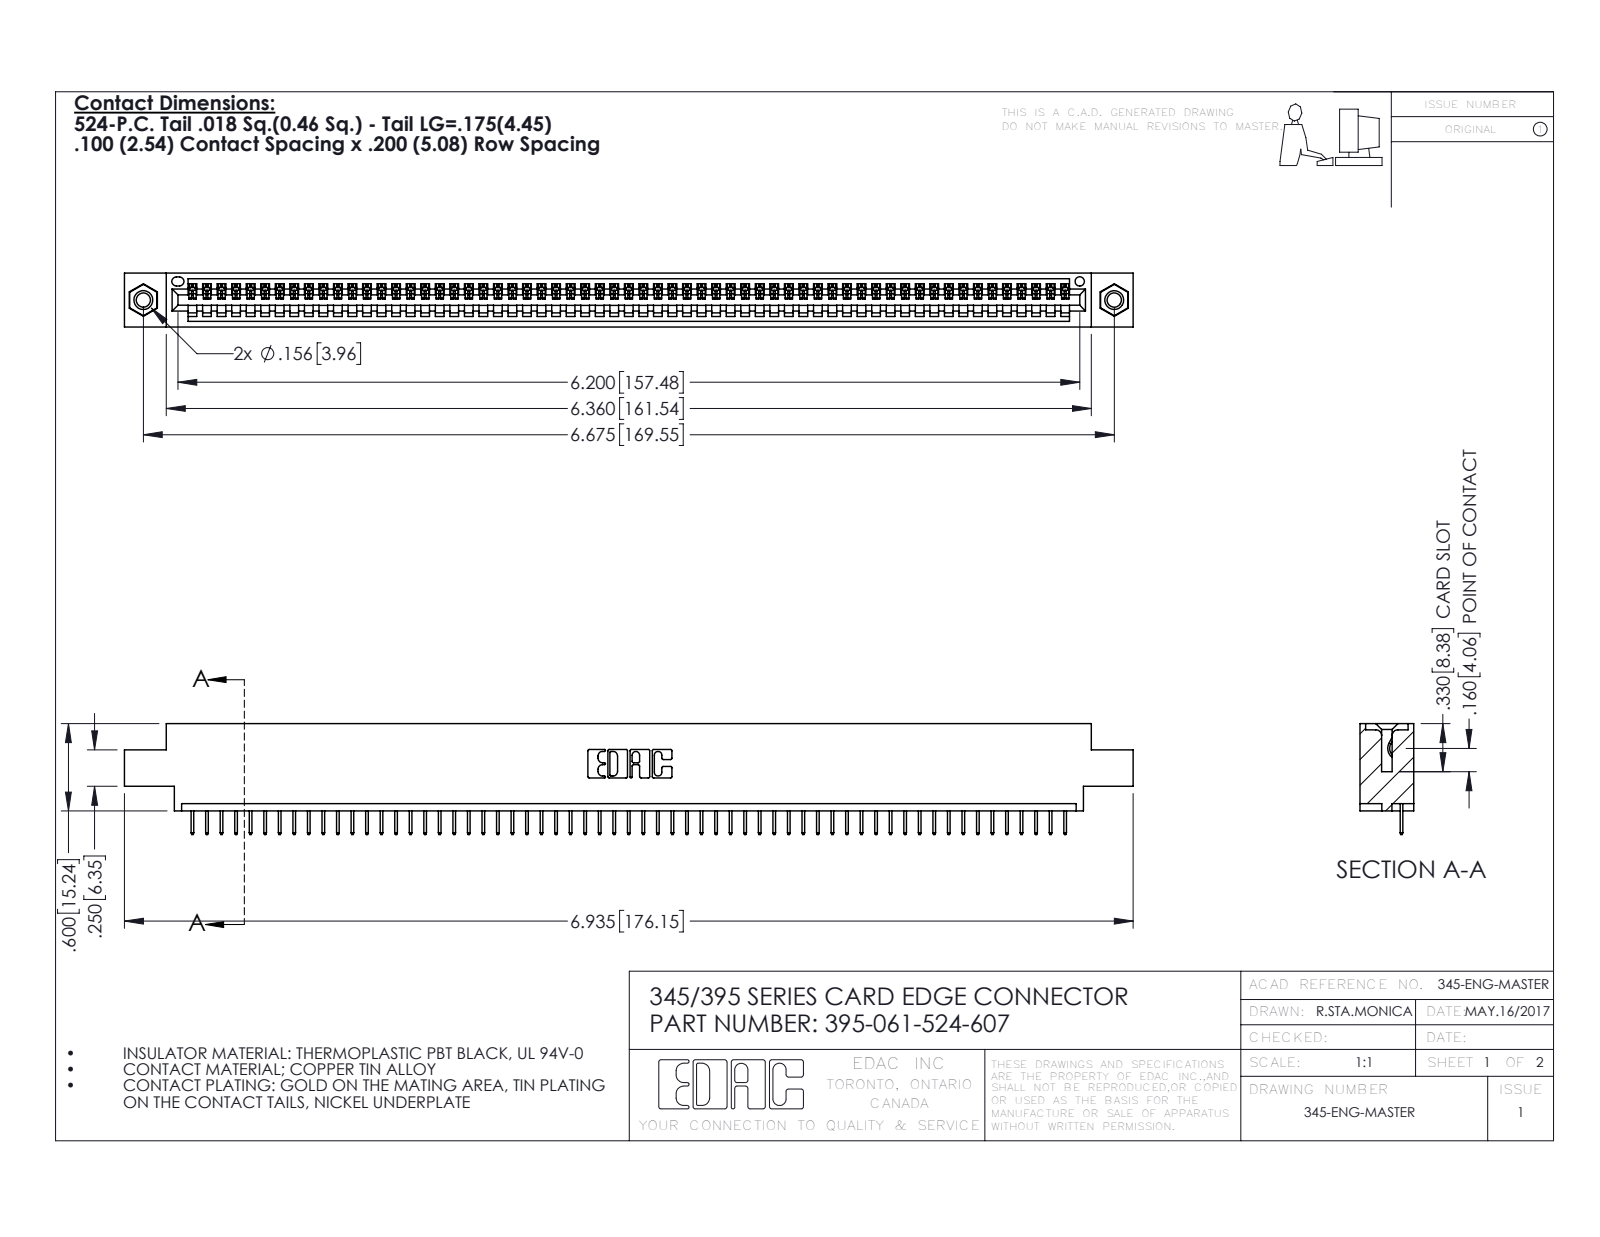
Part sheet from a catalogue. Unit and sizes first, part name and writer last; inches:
Units: inches
Overall size (bounding box): 6.935 × 0.762 × 0.37
Round holes (diameter × count): ⌀0.098 ×2, ⌀0.125 ×2, ⌀0.156 ×2, ⌀0.064 ×1
Round bosses / shafts (diameter × count): ⌀0.155 ×2
Partial cylindrical surfaces — rounded edges, fillets, slot ends (radius × count): R0.006 ×122, R0.01 ×22, R0.007 ×6, R0.031 ×6, R0.026 ×3, R0.031 ×2, R0.04 ×2, R0.014 ×1
Main face-to-face distances: 0.072, 0.298, 0.37, 0.2, 0.098, 0.272, 0.025, 0.225, 0.072, 0.175
Hole centre spacings: 0.27, 6.439, 6.675
Volume: 1.008 in³ · Surface area: 33.48 in²
Bodies: 64 solids, 3972 faces (2922 planar, 1034 cylindrical, 16 other)
Part name (STEP PRODUCT): 345 Part_0.170 Offset - 0.156 Dia-TI; 345-292-001_345-293-124; 395-061-524-607; 345-250-001_345-250-005-103
STEP written by: SolidWorks 2016 (CONFIG_CONTROL_DESIGN)
